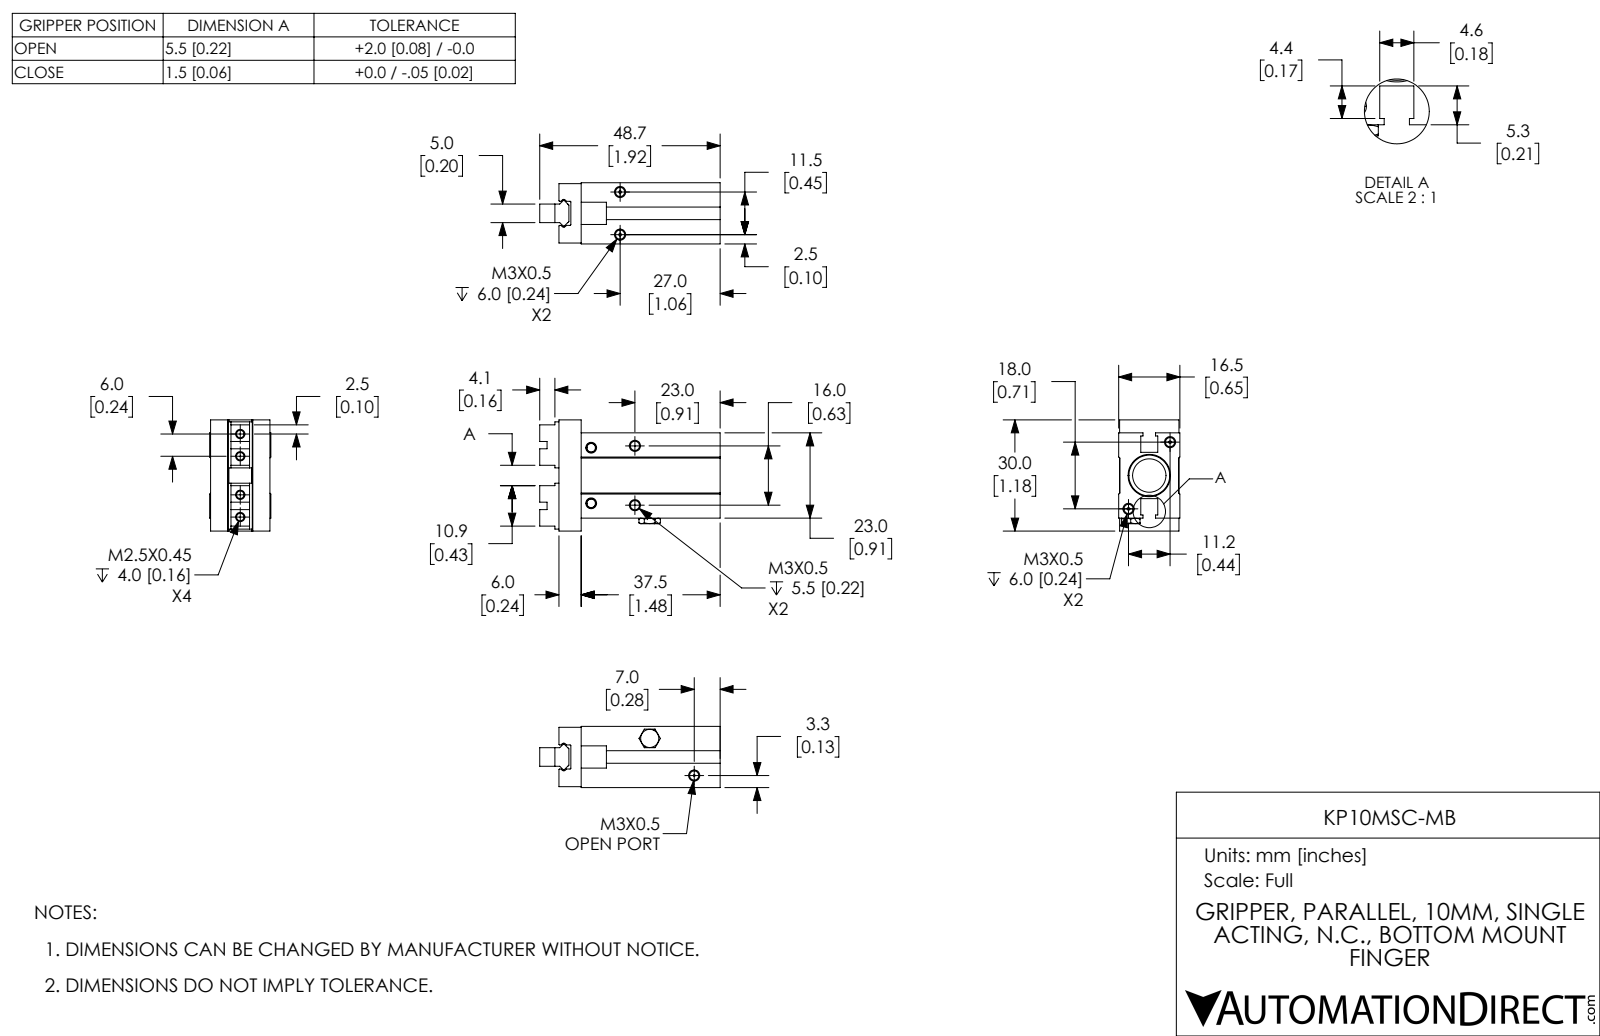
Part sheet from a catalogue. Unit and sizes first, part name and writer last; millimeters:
Units: millimetres
Overall size (bounding box): 48.7 × 30 × 16.5
Round holes (diameter × count): ⌀2.46 ×4, ⌀2.46 ×4, ⌀0.5 ×2, ⌀2.01 ×2, ⌀3.02 ×2, ⌀9 ×1, ⌀11 ×1
Partial cylindrical surfaces — rounded edges, fillets, slot ends (radius × count): R0.2 ×4, R0.25 ×2, R0.75 ×2, R1.01 ×2, R1.01 ×2
Main face-to-face distances: 16.2, 5.25, 5, 10.25, 5.65, 5.95, 10.55, 5.5, 16.5, 23
Hole centre spacings: 6.02, 10.6, 11.2, 20.96, 8.04, 11.5, 13.4, 15.62
Volume: 14 273 mm³ · Surface area: 7 389 mm²
Bodies: 3 solids, 240 faces (126 planar, 56 cylindrical, 58 other)
Part name (STEP PRODUCT): KP10MSC-MB-1; KP10MSC-MB; KP10MSC-MB-3; KP10MSC-MB-2
STEP written by: SolidWorks 2017 (CONFIG_CONTROL_DESIGN)
